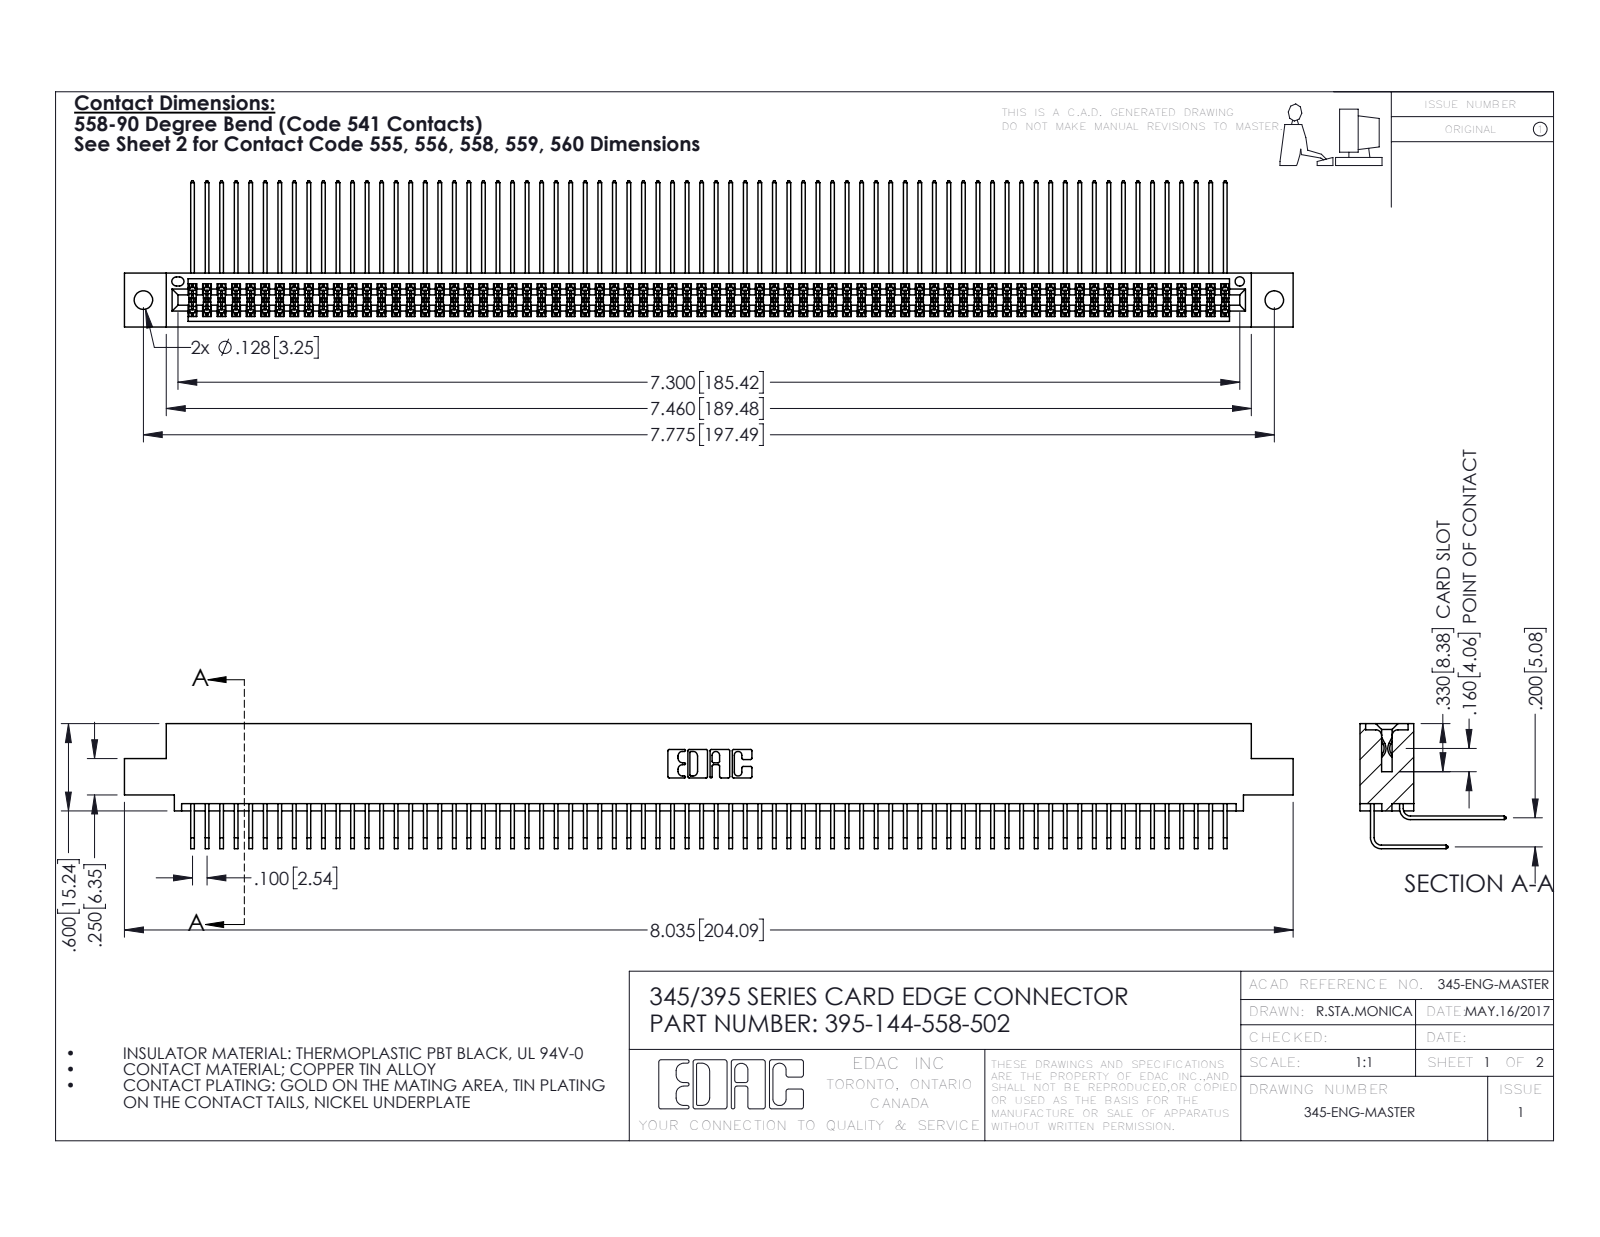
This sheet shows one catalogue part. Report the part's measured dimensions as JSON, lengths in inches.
{"part_name": "345 Part_0.110 Offset - 0.128 Dia; 345-292-001_558 559 Tail - 1; 345-292-001_558 Tail - 2; 395-144-558-502", "step_written_by": "SolidWorks 2016 (CONFIG_CONTROL_DESIGN)", "units": "inches", "bodies": {"solids": 145, "faces": 7618, "planar": 5124, "cylindrical": 2494, "other": 0}, "overall_size": [8.035, 1.005, 0.859], "volume_in3": 1.271, "surface_area_in2": 54.39, "round_holes": [[0.128, 2], [0.064, 1]], "partial_cylinders_radius": [[0.006, 216], [0.01, 22], [0.007, 6], [0.031, 6], [0.026, 3], [0.014, 2], [0.019, 2], [0.022, 2]], "face_to_face_distances": [0.072, 0.298, 0.2, 0.37, 0.098, 0.272, 0.025, 0.225, 0.025, 0.175], "hole_center_spacings": [0.27, 7.539, 7.775]}
